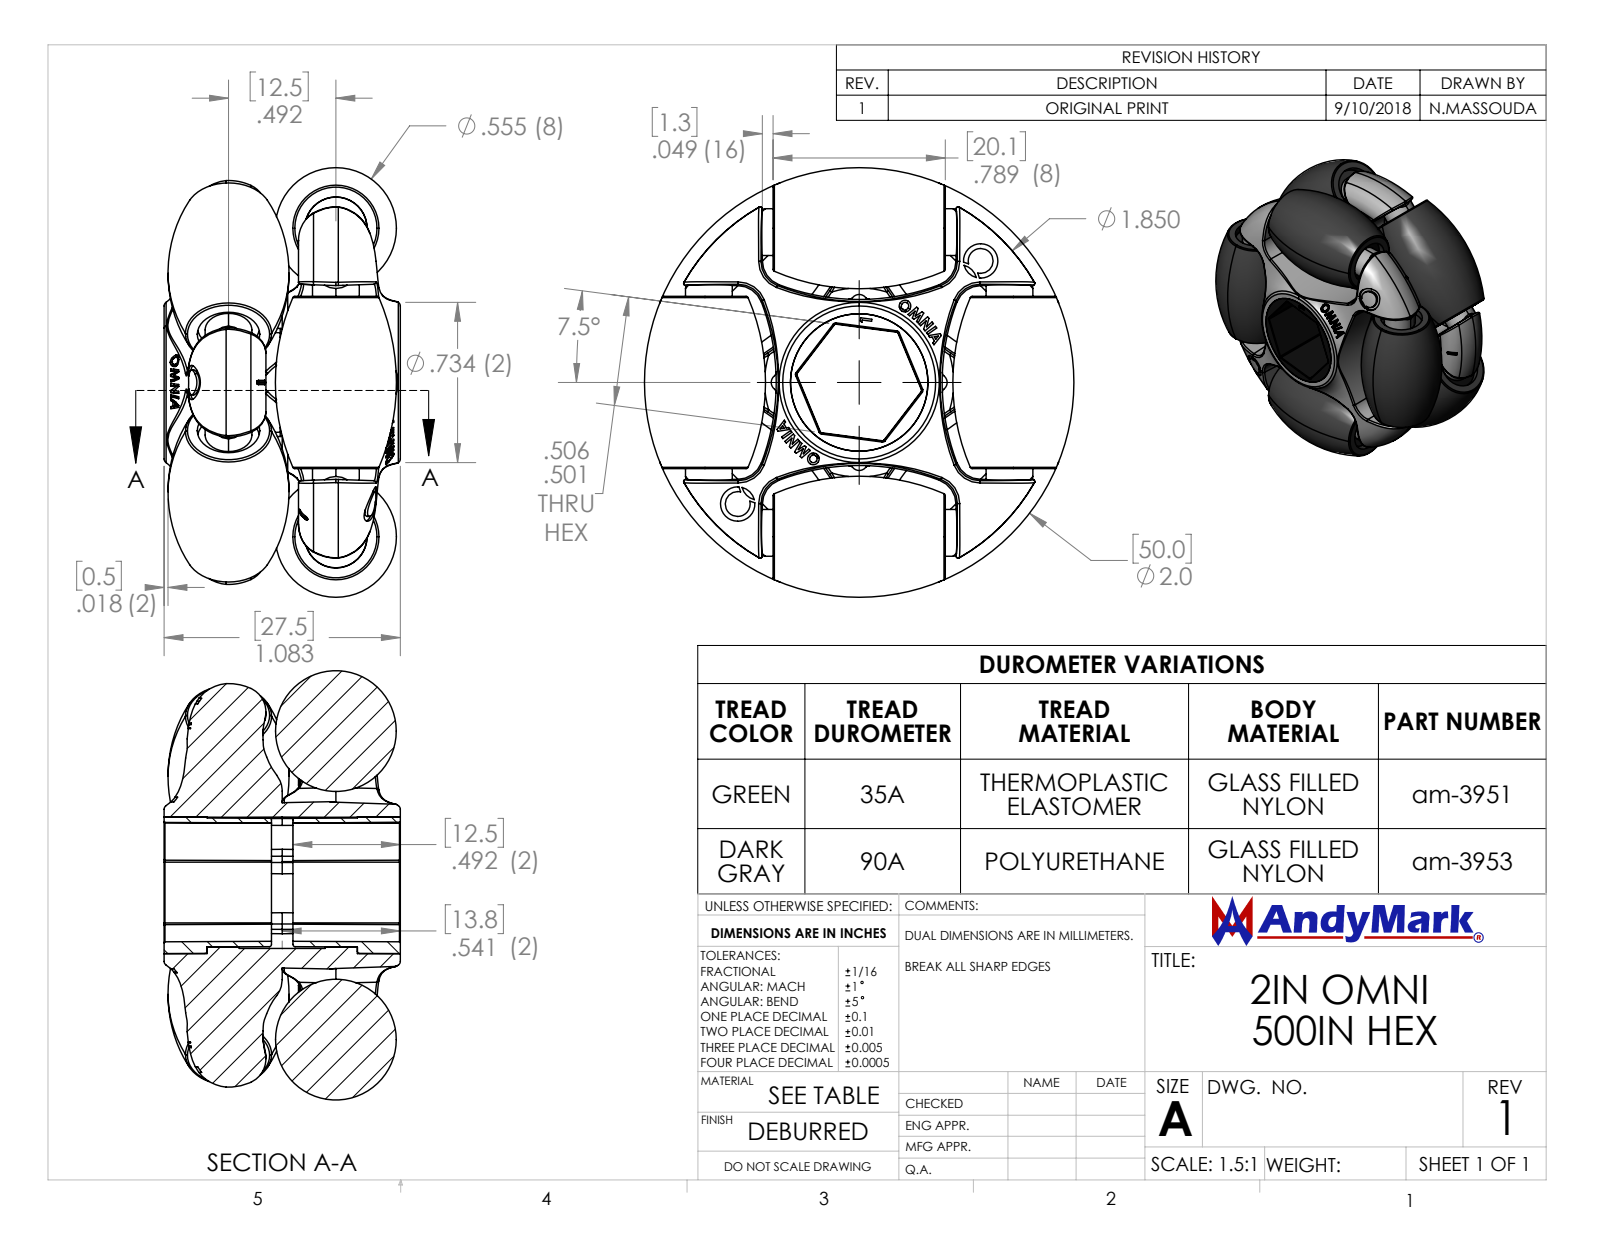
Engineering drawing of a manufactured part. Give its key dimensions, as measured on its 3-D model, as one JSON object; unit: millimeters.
{"part_name": "am-3951 am-3953 2in Omni 500in Hex; am-3904 14mm Hex to 500in Hex; 2in Omni 14mm Hex", "step_written_by": "SolidWorks 2018 (AUTOMOTIVE_DESIGN)", "units": "millimeters", "bodies": {"solids": 3, "faces": 1127, "planar": 326, "cylindrical": 137, "other": 664}, "overall_size": [49.99, 49.99, 27.5], "volume_mm3": 30754, "surface_area_mm2": 17341, "round_holes": [[4, 4], [16, 1]], "round_bosses_or_shafts": [[5.44, 6], [2.9, 4], [5.45, 2]], "partial_cylinders_radius": [[0.1, 12], [0.25, 12], [0.2, 8], [0.68, 4], [0.83, 4], [2, 4], [2.34, 4], [7.4, 1]], "face_to_face_distances": [13.31, 0.57, 13.98, 12.74, 0.58, 13.32, 13.89, 0.66, 0.67, 18.87], "hole_center_spacings": [20, 40, 15.31, 15.32, 36.95, 36.96]}
